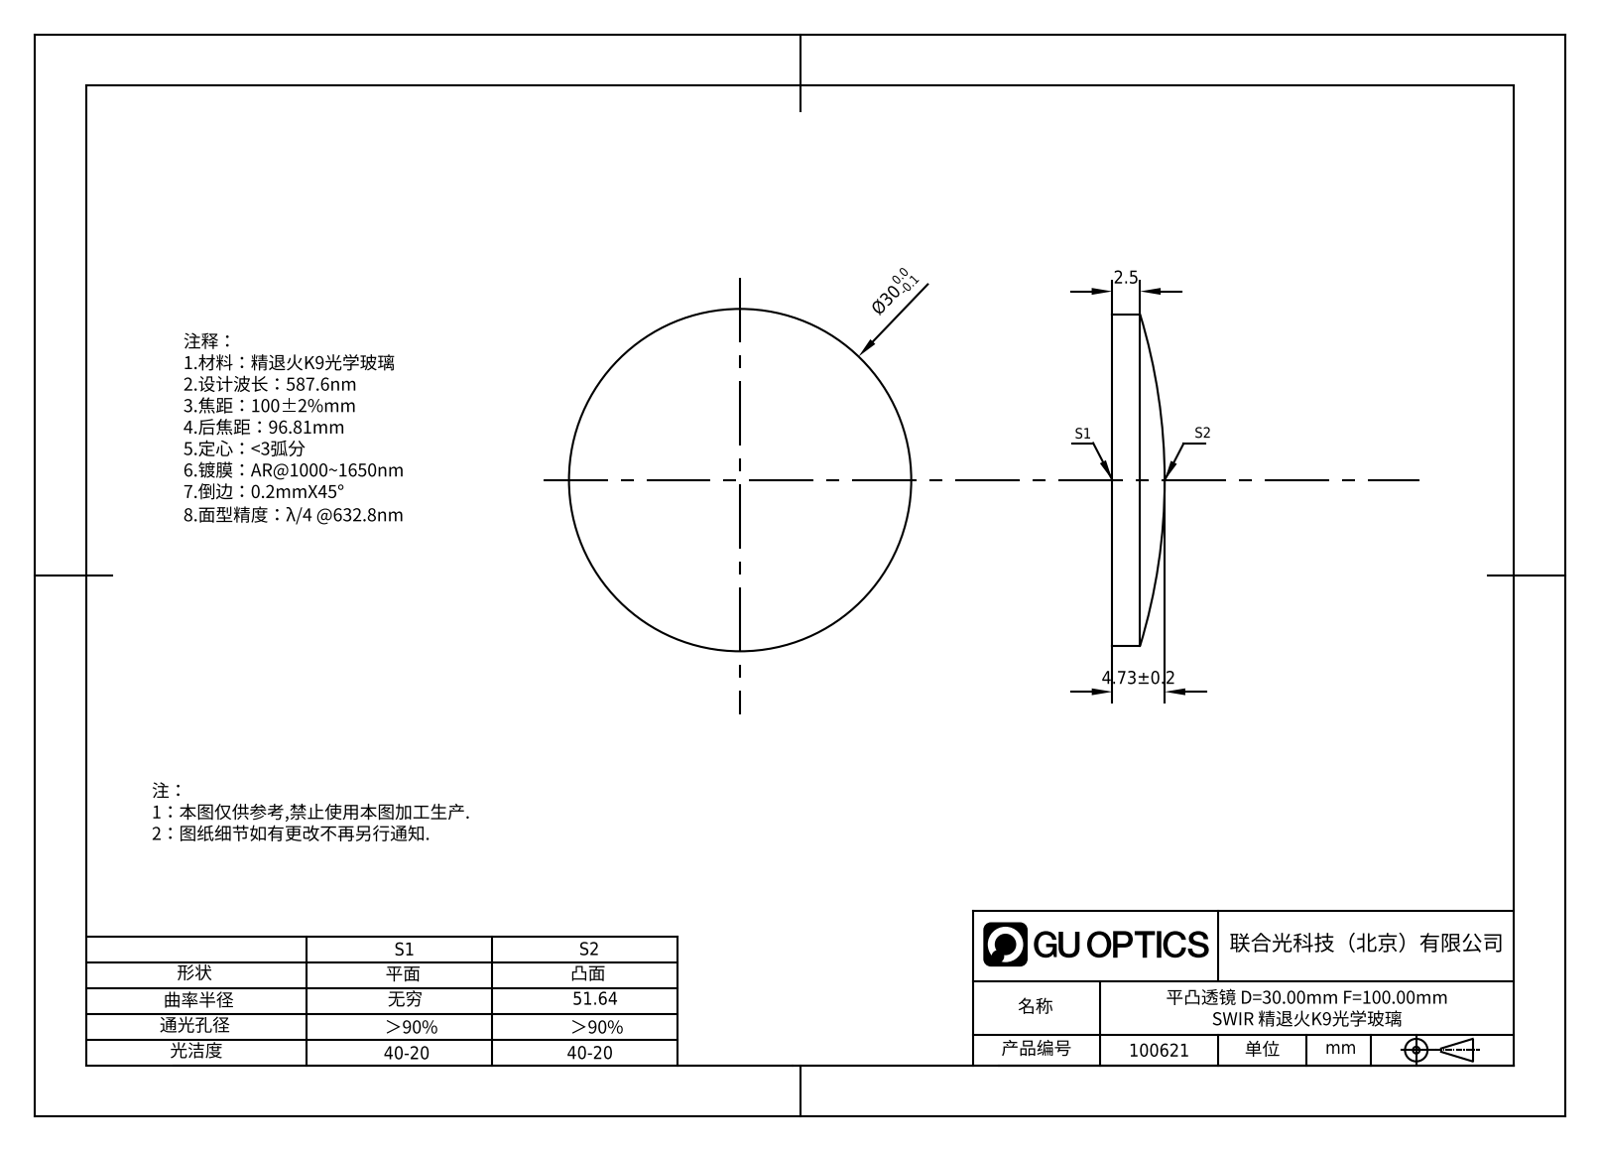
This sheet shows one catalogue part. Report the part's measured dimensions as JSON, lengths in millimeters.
{"part_name": "100598", "step_written_by": "SolidWorks 2020 (CONFIG_CONTROL_DESIGN)", "units": "millimeters", "bodies": {"solids": 1, "faces": 5, "planar": 1, "cylindrical": 2, "other": 2}, "overall_size": [30, 30, 4.73], "volume_mm3": 2561, "surface_area_mm2": 1665, "round_bosses_or_shafts": [[30, 1]]}
